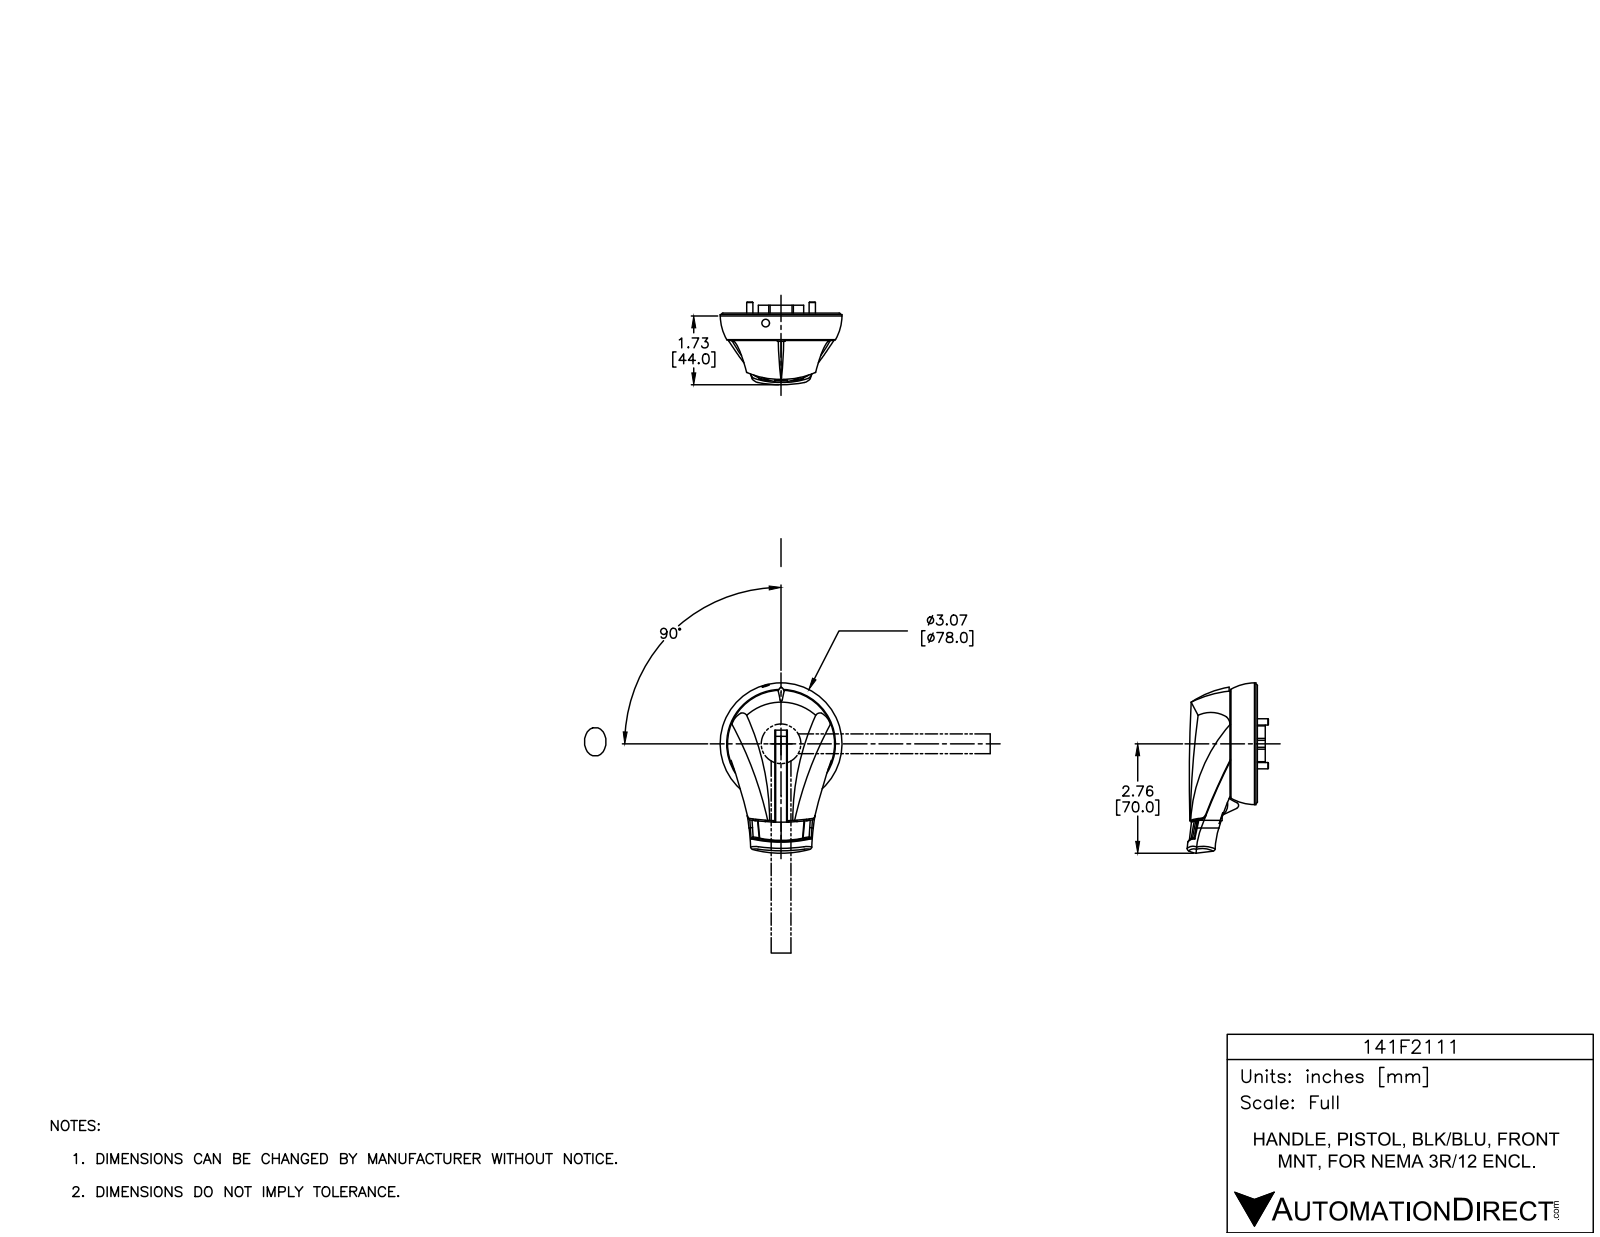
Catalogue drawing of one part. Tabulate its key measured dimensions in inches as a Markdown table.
| quantity | value |
| --- | --- |
| part name | 141F2111 |
| STEP written by | SolidWorks 2015 (AUTOMOTIVE_DESIGN) |
| units | inches |
| bodies | 8 solids, 1516 faces (810 planar, 548 cylindrical, 158 other) |
| overall size | 4.291 × 3.07 × 2.046 |
| volume | 7.72 in³ |
| surface area | 79.65 in² |
| round holes (diameter × count) | 0.157 × 6, 0.339 × 4, 0.425 × 4, 0.03 × 3, 0.169 × 2, 0.362 × 2, 0.118 × 1, 0.189 × 1, 2.992 × 1 |
| round bosses / shafts (diameter × count) | 0.02 × 11, 0.335 × 4, 0.315 × 4, 0.089 × 3, 0.069 × 3, 0.228 × 2, 2.819 × 1, 2.701 × 1 |
| partial cylindrical surfaces (radius × count) | 0.01 × 221, 0.015 × 20, 0.034 × 20, 0.03 × 15, 0.039 × 4, 0.025 × 3, 5.437 × 3, 0.079 × 2 |
| main face-to-face distances | 0.024, 0.701, 0.713, 0.689, 0.035, 0.102, 0.276, 0.173, 0.244, 0.047 |
| hole center spacings | 0.961, 0.309, 0.669, 1.098, 1.102, 1.203, 1.575, 1.881 |
